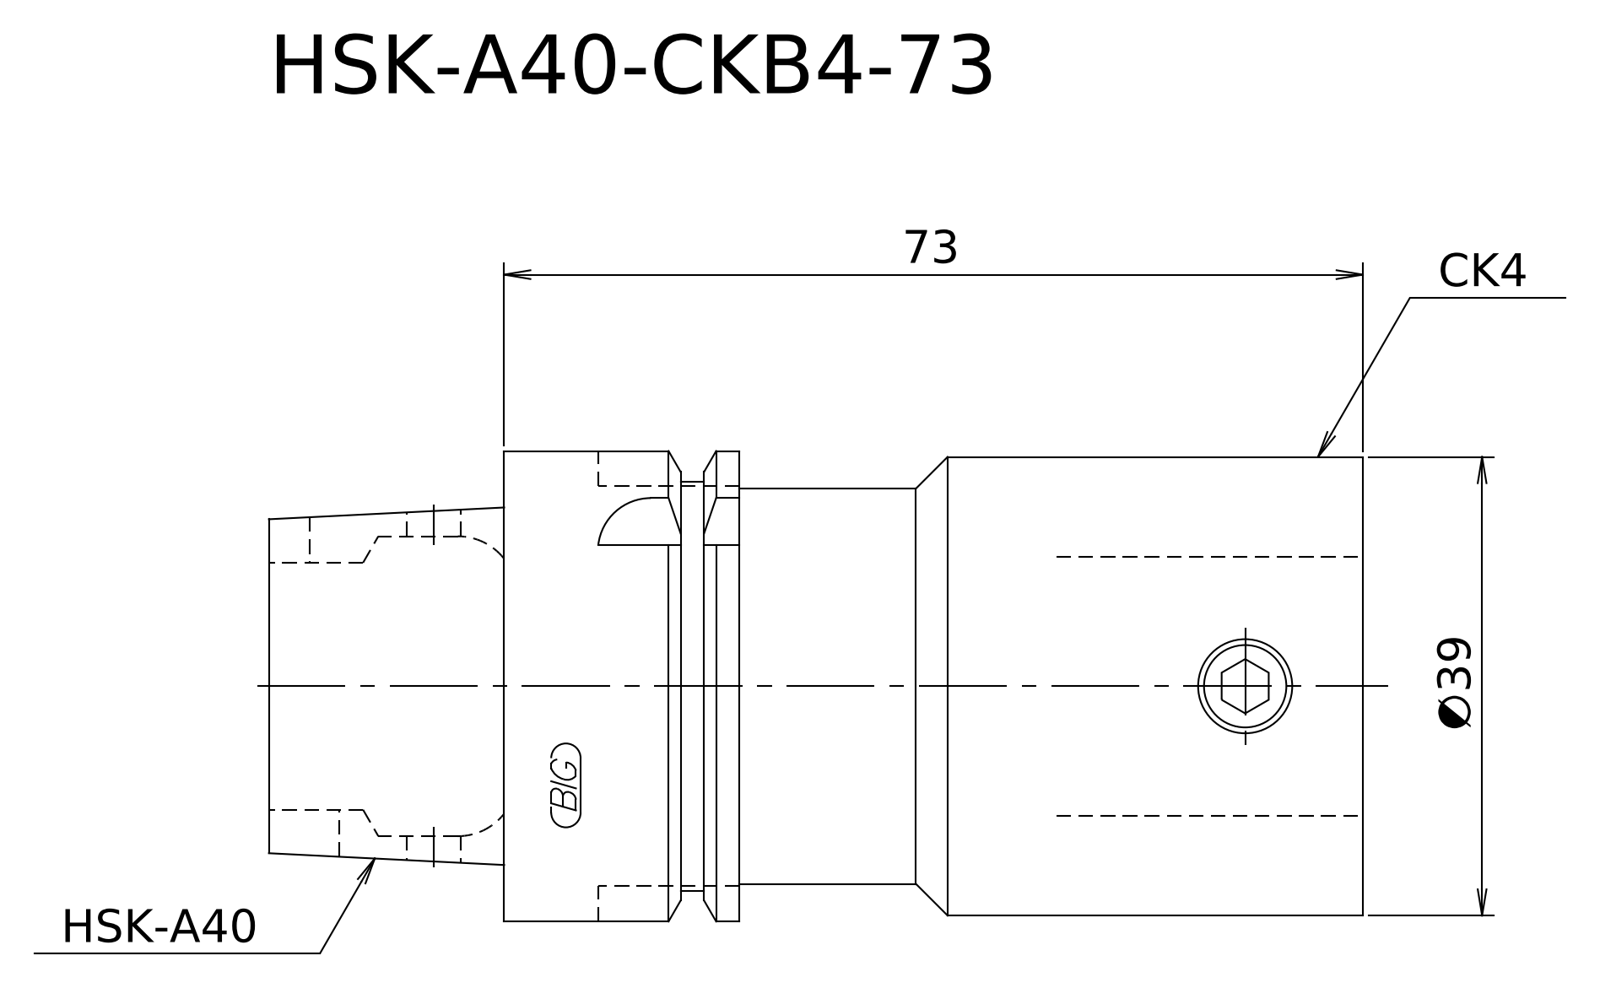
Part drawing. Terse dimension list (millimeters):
written by: Kubotek KeyCreator V8.5.1 (14335) (CONFIG_CONTROL_DESIGN)
unit: mm
bodies: 1 solid, 16 faces (6 planar, 6 cylindrical, 4 other)
size: 93 × 40 × 40
volume: 96 148 mm³; area: 13 830 mm²
bosses: 1× ⌀40, 1× ⌀39, 1× ⌀34.8, 1× ⌀33.6, 1× ⌀30.25
face distances: 20, 93, 73, 53, 40, 56, 3, 17, 37, 58
